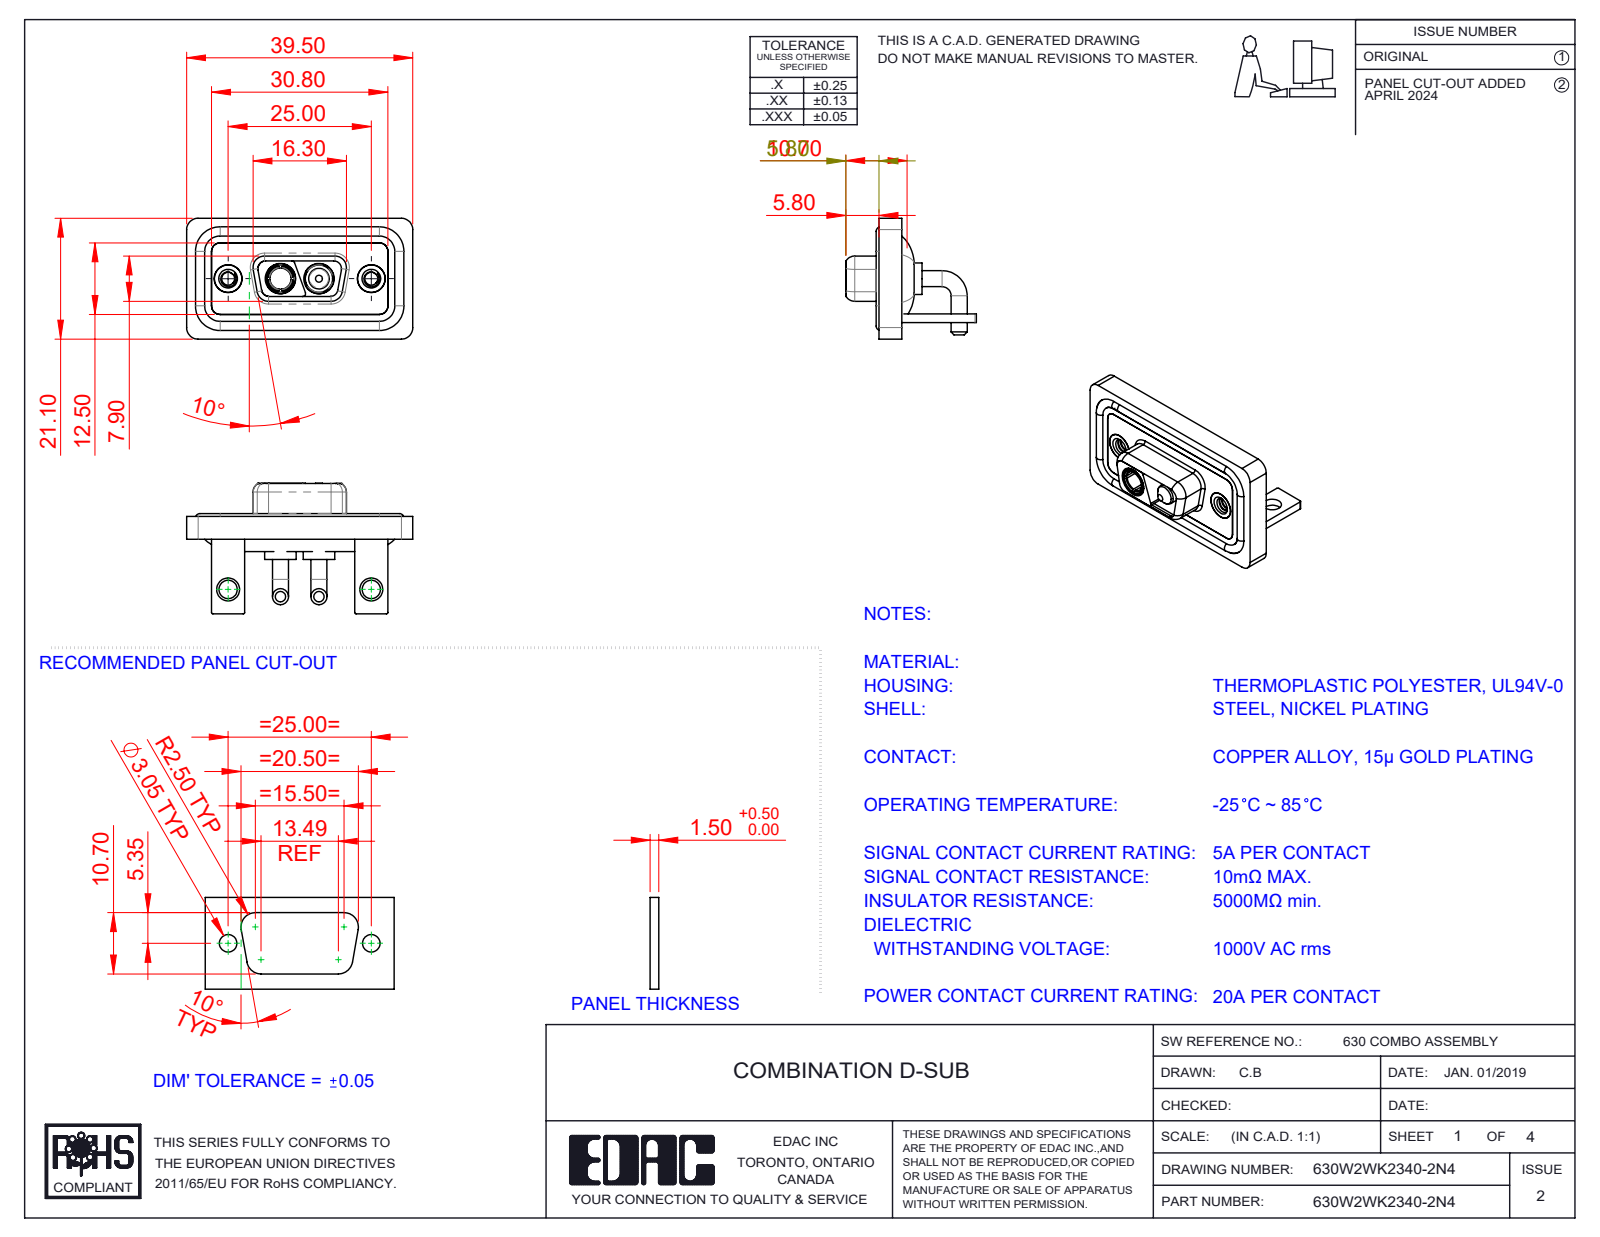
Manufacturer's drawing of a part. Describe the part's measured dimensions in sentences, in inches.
The part is named "Power Socket_20A RA; 630Combo Stabilizer Bracket_50 Contacts; 630Combo Housing_2WK2; Power Pin_20A RA (+5 more)". Its 3-D file was written by "SolidWorks 2023 (CONFIG_CONTROL_DESIGN)". It is 13 solids with 556 faces: 164 planar, 259 cylindrical and 133 other. Overall it measures 1.555 by 0.898 by 0.831 inches. Its volume is 0.31 cubic inches and its surface area 12.75 square inches. Round holes: 4 of diameter 0.191, 2 of diameter 0.089, 2 of diameter 0.126, 2 of diameter 0.157, 2 of diameter 0.159, 2 of diameter 0.197, 2 of diameter 0.209, 1 of diameter 0.146. Round bosses or shafts: 4 of diameter 0.11, 4 of diameter 0.063, 2 of diameter 0.217, 2 of diameter 0.205, 2 of diameter 0.195, 2 of diameter 0.189, 2 of diameter 0.187, 2 of diameter 0.148. Partial cylindrical surfaces (rounded edges, fillets, slot ends): 19 of radius 0.079, 18 of radius 0.059, 16 of radius 0.01, 8 of radius 0.053, 8 of radius 0.063, 7 of radius 0.02, 4 of radius 0.024, 4 of radius 0.026. The main face-to-face distances are 0.016, 0.114, 0.059, 0.043, 0.146, 0.071, 0.031, 0.098, 0.063, 0.122. The hole center spacings are 0.36, 0.624, 0.984, 0.265.
